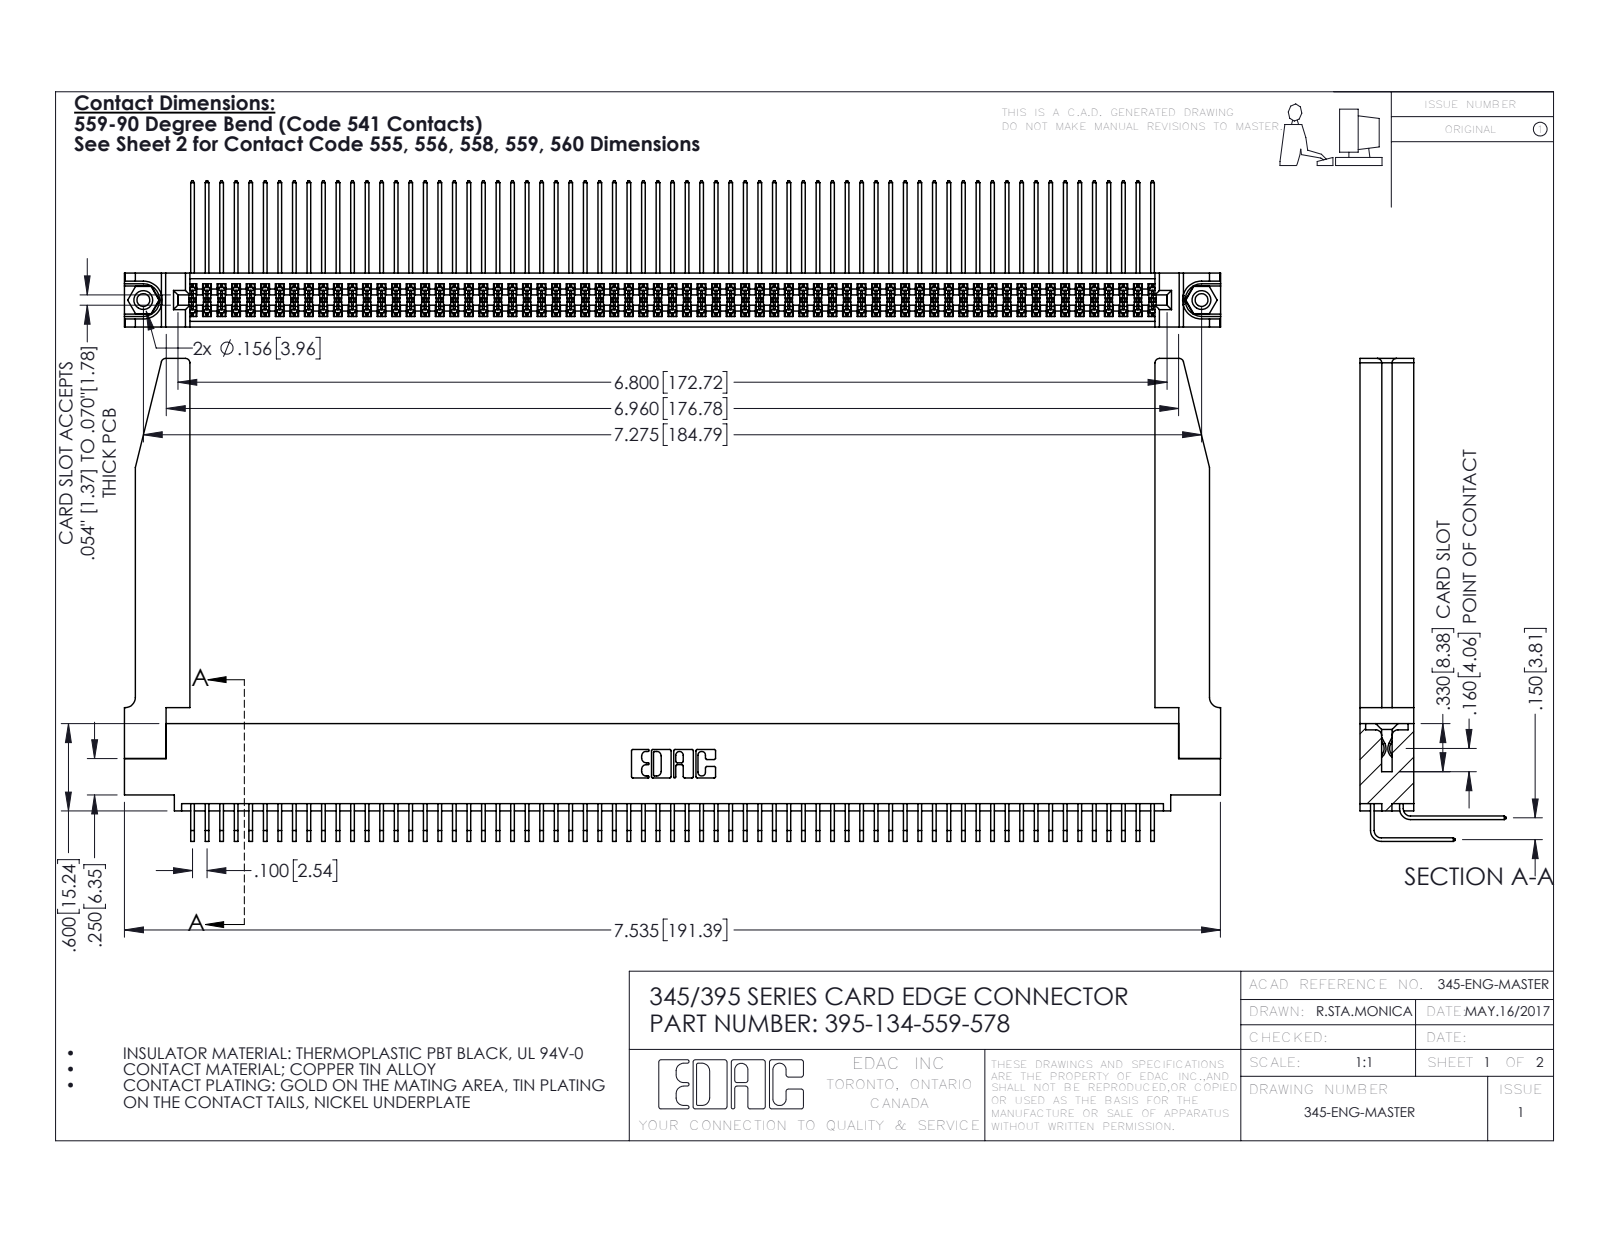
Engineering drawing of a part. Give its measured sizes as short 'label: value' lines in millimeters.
name: 345 Part_0.110 Offset - 0.156 Dia-TH; 345-292-001_558 559 Tail - 1; 345-250-001_345-250-001-102; 345-292-001_559 Tail - 2 (+2 more)
written by: SolidWorks 2016 (CONFIG_CONTROL_DESIGN)
unit: mm
bodies: 139 solids, 7332 faces (4916 planar, 2364 cylindrical, 52 other)
size: 191.4 × 84.3 × 25.5
volume: 27 300 mm³; area: 39 920 mm²
holes: 2× ⌀2.3, 2× ⌀3.2, 2× ⌀4, 1× ⌀1.6
bosses: 2× ⌀3.9
rounds: 201× R0.2, 22× R0.3, 8× R0.8, 6× R0.2, 6× R0.8, 3× R0.7, 2× R0.4, 2× R0.5
face distances: 1.8, 7.6, 9.4, 2.5, 6.9, 0.6, 5.1, 5.7, 4.4, 3.8
hole spacings: 6.9, 178.8, 184.8
